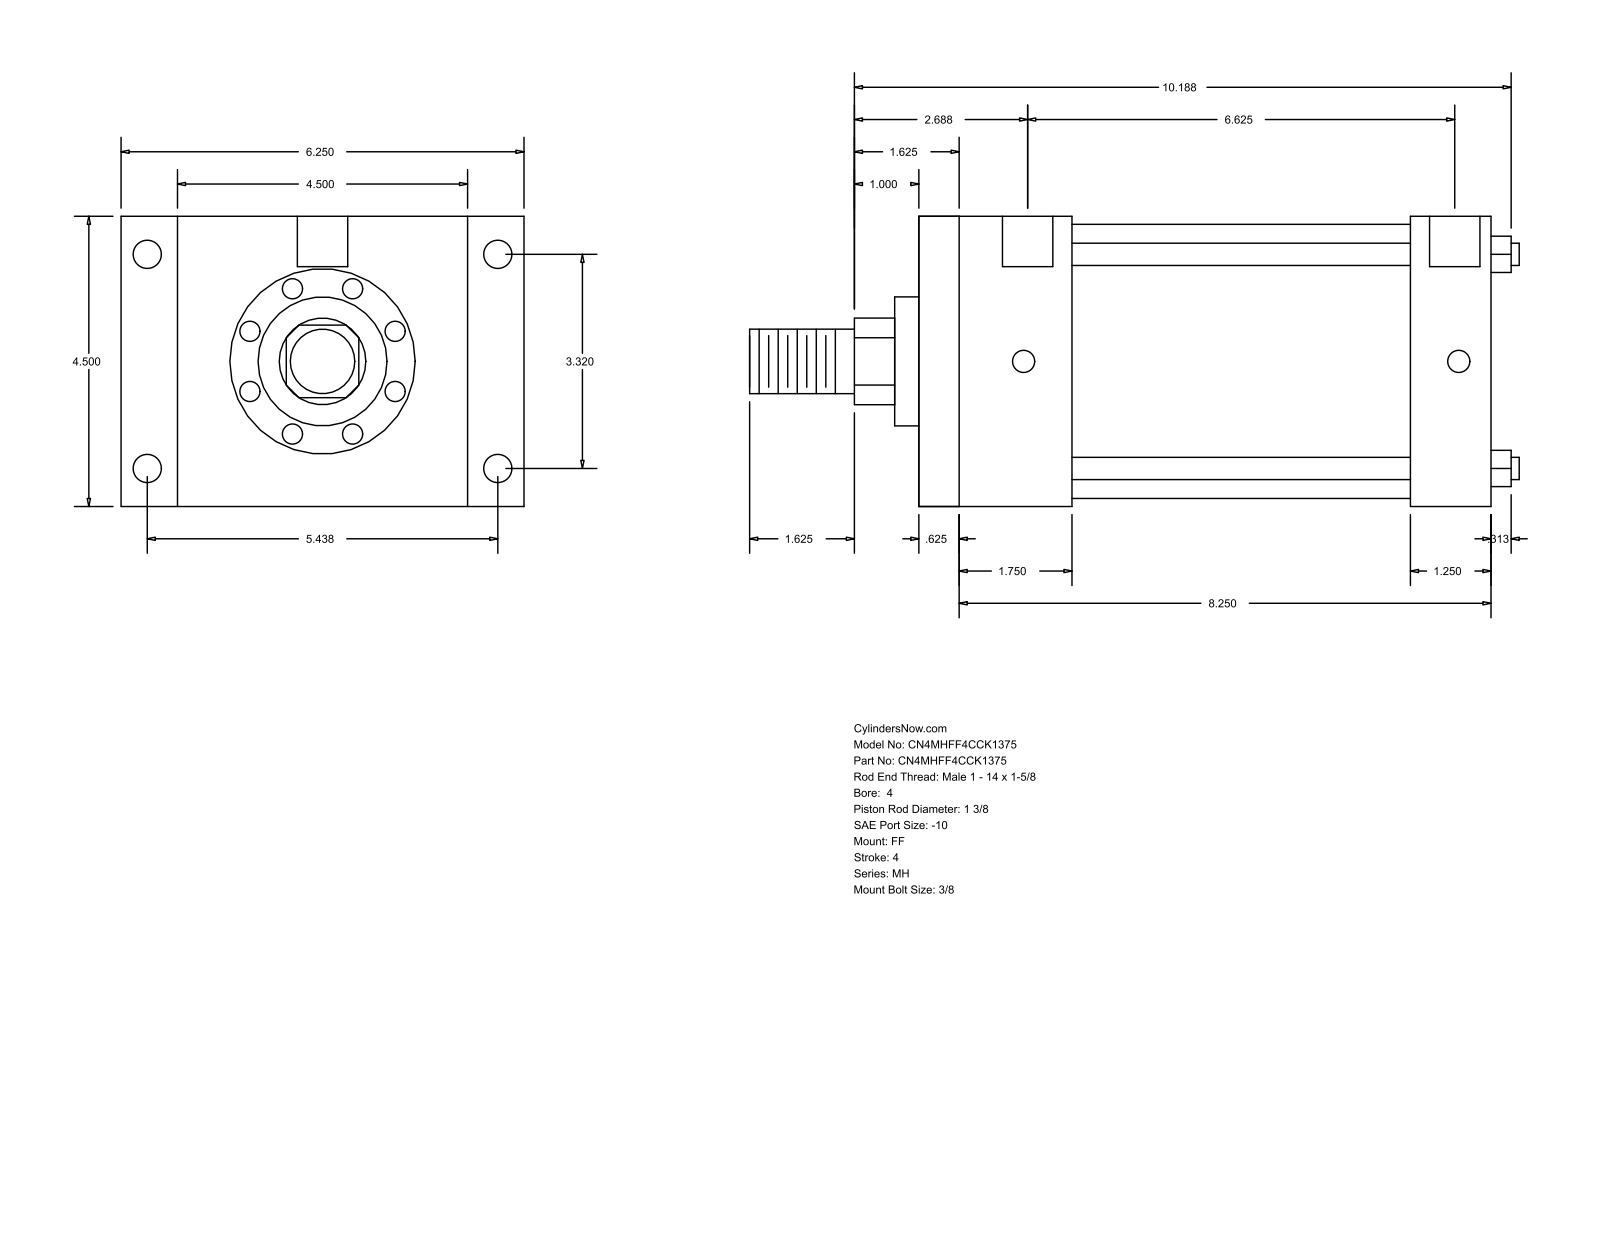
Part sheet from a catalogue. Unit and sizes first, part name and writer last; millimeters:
Units: millimetres
Overall size (bounding box): 303.21 × 158.75 × 114.3
Round holes (diameter × count): ⌀8.73 ×4, ⌀11.13 ×4, ⌀19.84 ×2
Round bosses / shafts (diameter × count): ⌀8.76 ×4, ⌀107.95 ×1, ⌀50.8 ×1, ⌀34.92 ×1, ⌀25.4 ×1
Partial cylindrical surfaces — rounded edges, fillets, slot ends (radius × count): R17.06 ×1
Main face-to-face distances: 114.3, 225.42, 15.87, 209.55, 60.32, 44.45, 165.1, 193.67, 177.8, 133.35
Hole centre spacings: 84.32, 138.12, 161.82, 171.45, 1.58, 1.59, 168.28, 169.86
Bodies: 0 solids, 92 faces (64 planar, 28 cylindrical, 0 other)
Part name (STEP PRODUCT): MH_FF__0400_1.375
STEP written by: GSSL Pune (CONFIG_CONTROL_DESIGN)
